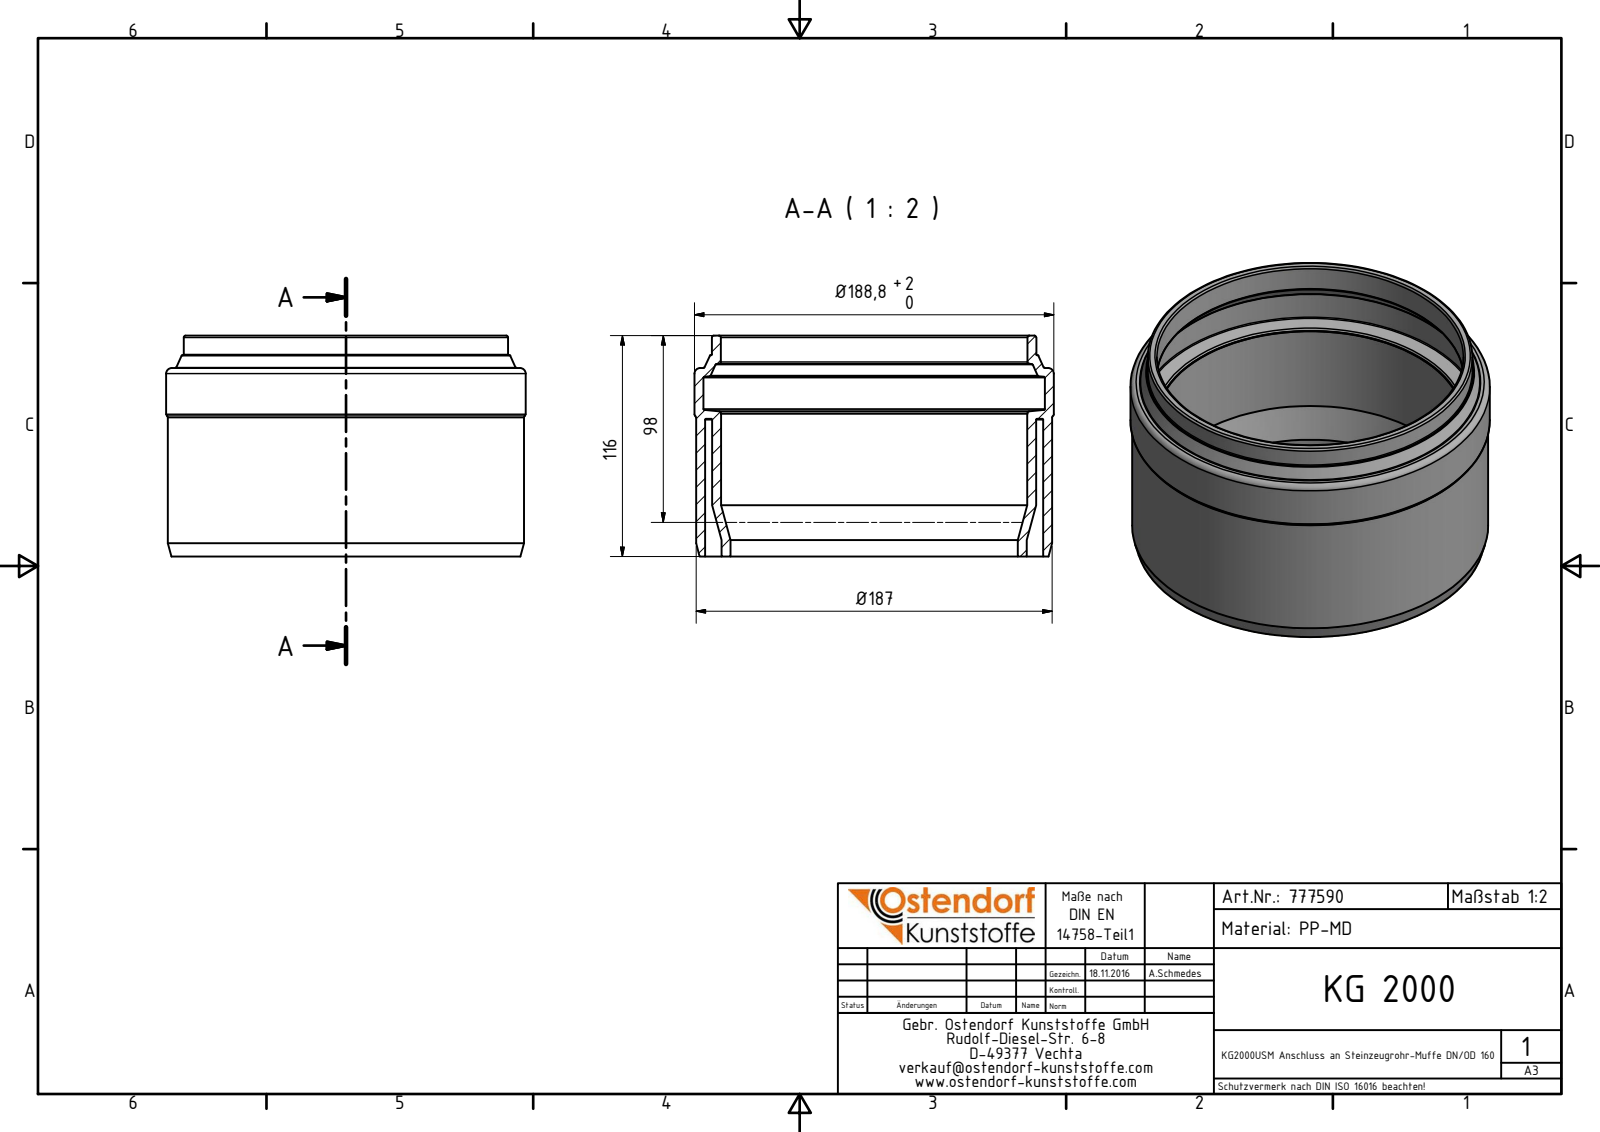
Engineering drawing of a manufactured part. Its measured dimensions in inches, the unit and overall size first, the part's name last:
Units: inches
Overall size (bounding box): 7.433 × 7.433 × 4.567
Round holes (diameter × count): ⌀5.941 ×1, ⌀6.327 ×1, ⌀6.339 ×1, ⌀6.992 ×1, ⌀7.063 ×1
Round bosses / shafts (diameter × count): ⌀7.433 ×1, ⌀7.362 ×1, ⌀6.709 ×1, ⌀6.697 ×1, ⌀6.311 ×1
Main face-to-face distances: 2.846, 4.567, 1.72, 3.898, 1.051, 0.669, 4.161, 1.315, 0.264, 0.406
Volume: 31.44 in³ · Surface area: 347.4 in²
Bodies: 1 solid, 42 faces (7 planar, 11 cylindrical, 24 other)
Part name (STEP PRODUCT): 777590 KG2000USM Anschluss an Steinzeugrohr-Muffe DN_OD 160
STEP written by: Autodesk Inventor 2016 (AUTOMOTIVE_DESIGN)
